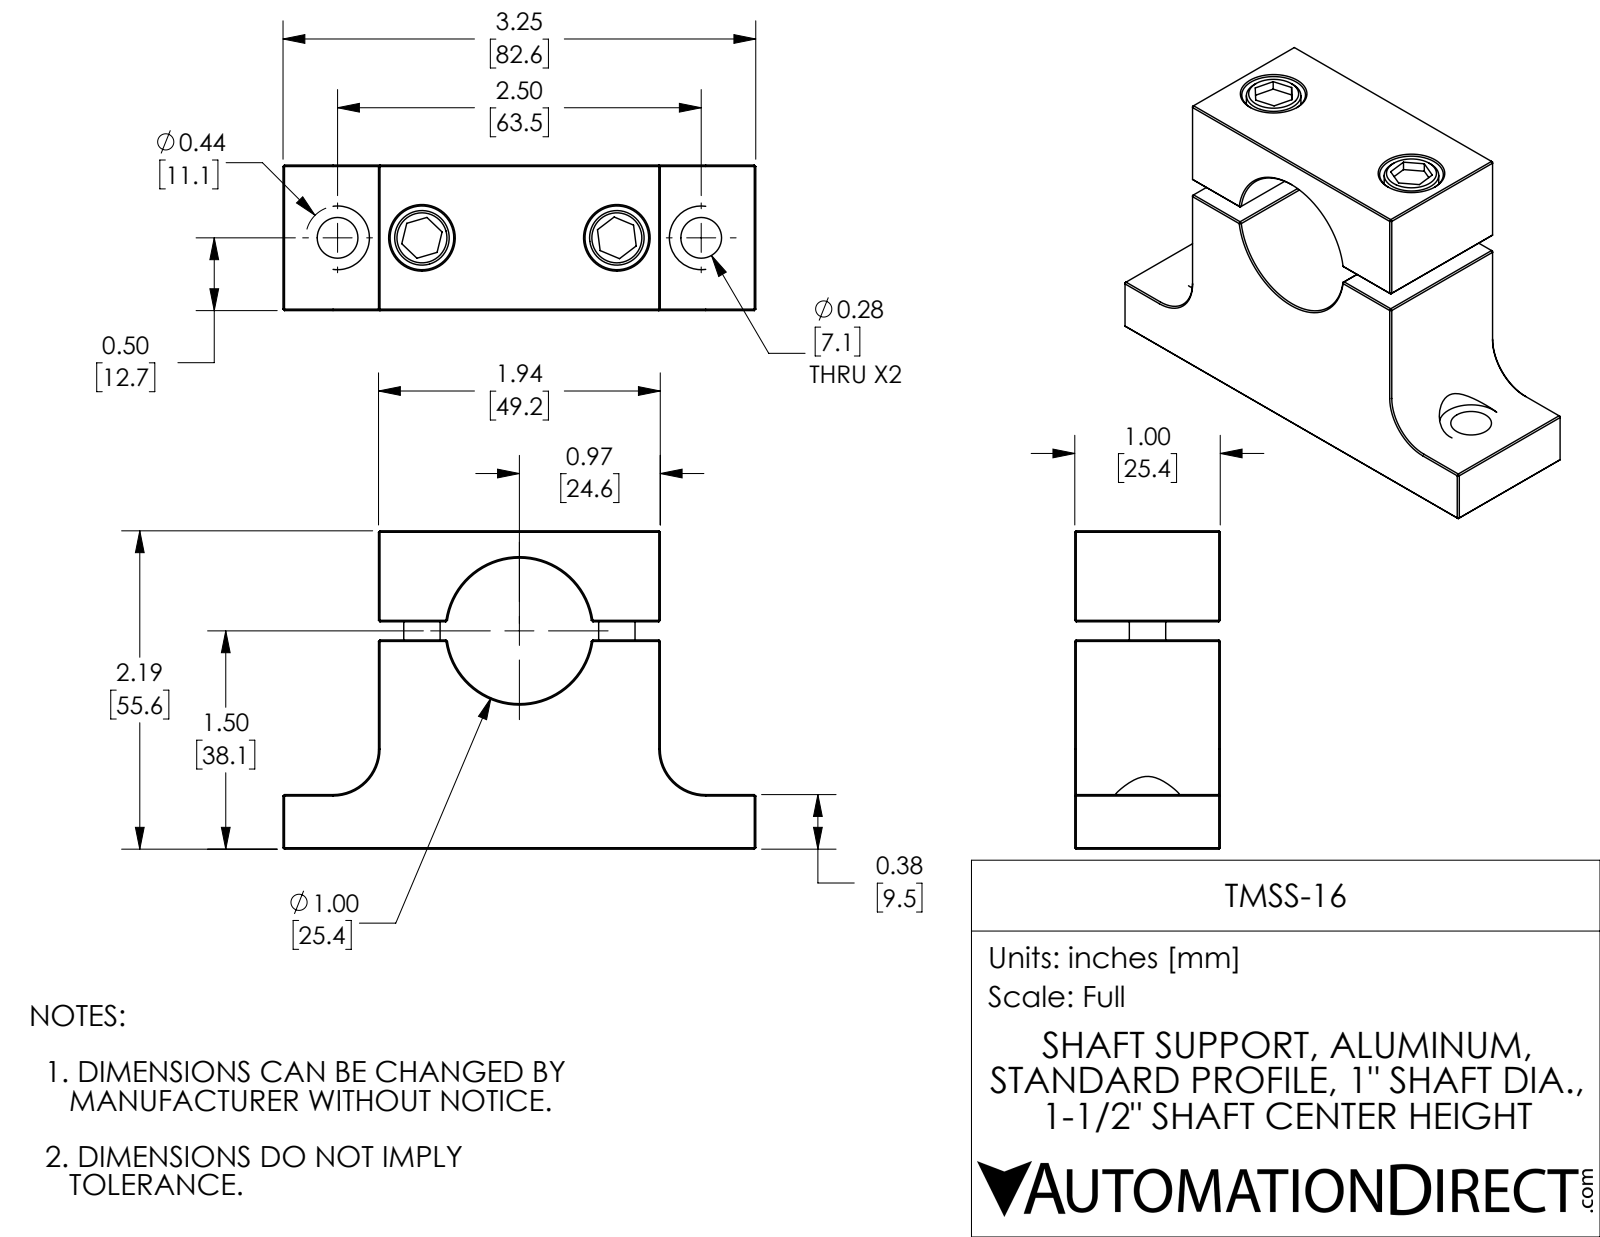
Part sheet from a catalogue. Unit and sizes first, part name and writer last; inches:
Units: inches
Overall size (bounding box): 3.25 × 2.188 × 1
Round holes (diameter × count): ⌀0.196 ×2, ⌀0.266 ×2, ⌀0.28 ×2, ⌀0.438 ×2, ⌀1 ×1
Round bosses / shafts (diameter × count): ⌀0.375 ×2, ⌀0.25 ×2
Partial cylindrical surfaces — rounded edges, fillets, slot ends (radius × count): R0.219 ×2, R0.313 ×2
Main face-to-face distances: 1, 2.187, 1.937, 1.437, 0.75, 1.563, 0.125, 0.625, 0.375, 1.062
Hole centre spacings: 0.58, 1.92, 1.34, 2.5
Volume: 3.757 in³ · Surface area: 28.47 in²
Bodies: 4 solids, 165 faces (110 planar, 31 cylindrical, 24 other)
Part name (STEP PRODUCT): TMSS-16
STEP written by: SolidWorks 2017 (AUTOMOTIVE_DESIGN)
